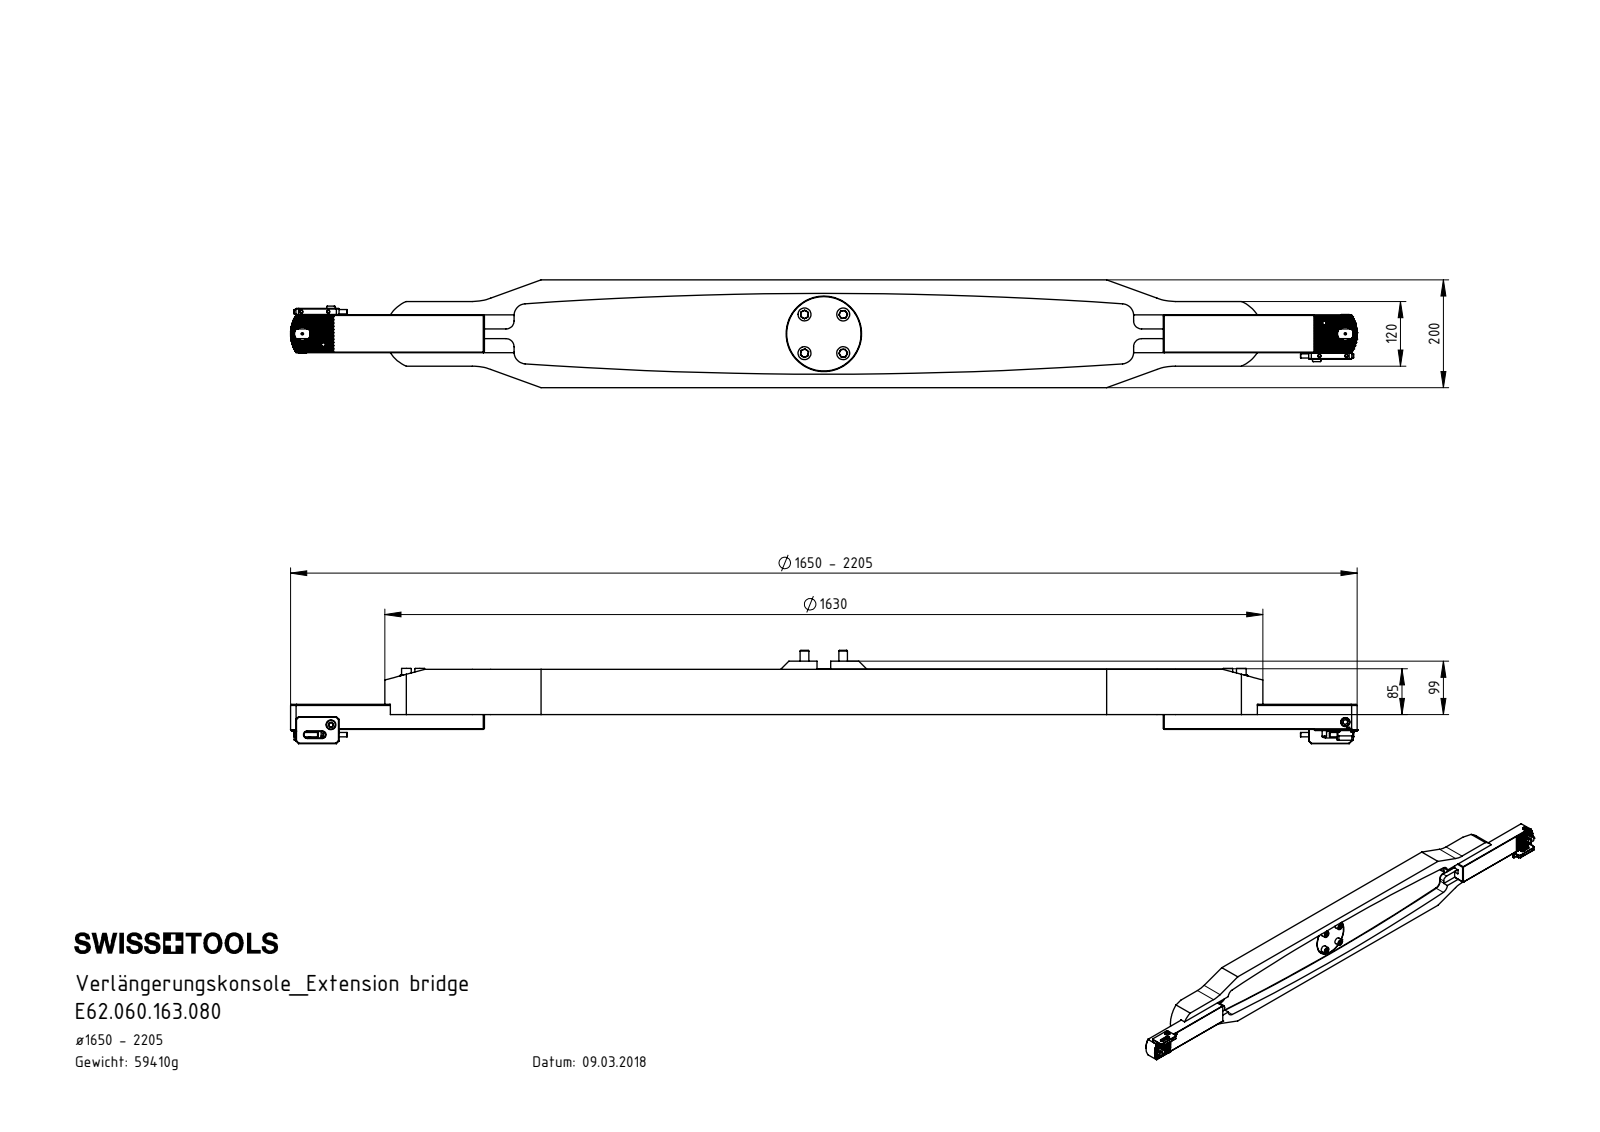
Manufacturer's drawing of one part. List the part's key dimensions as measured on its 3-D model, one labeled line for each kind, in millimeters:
Part name (STEP PRODUCT): E62.060.163.080; VK1-ER7.001.012_A; ISO 4762 - M12 x 80; ISO 7090 - 12 (+8 more)
STEP written by: SolidWorks 2017 (CONFIG_CONTROL_DESIGN)
Units: millimetres
Bodies: 46 solids, 2145 faces (916 planar, 736 cylindrical, 493 other)
Overall size (bounding box): 1980 × 200 × 173
Volume: 17 080 000 mm³ · Surface area: 1 497 000 mm²
Round holes (diameter × count): ⌀18 ×42, ⌀10.2 ×40, ⌀13 ×16, ⌀5 ×4, ⌀6 ×4, ⌀6.8 ×4, ⌀12 ×4, ⌀17 ×4, ⌀2 ×2, ⌀8 ×2, ⌀8.5 ×2, ⌀10.5 ×2
Round bosses / shafts (diameter × count): ⌀24 ×12, ⌀16 ×8, ⌀12 ×4, ⌀10 ×2, ⌀8 ×2, ⌀138 ×1
Partial cylindrical surfaces — rounded edges, fillets, slot ends (radius × count): R0.14 ×33, R2 ×22, R22 ×12, R15 ×6, R1.5 ×4, R5.5 ×4, R6 ×4, R8 ×4
Main face-to-face distances: 32, 65, 13, 45, 71, 84, 39, 200, 40, 135
Hole centre spacings: 25, 47.17, 50, 64.03, 40, 75, 85, 1450
